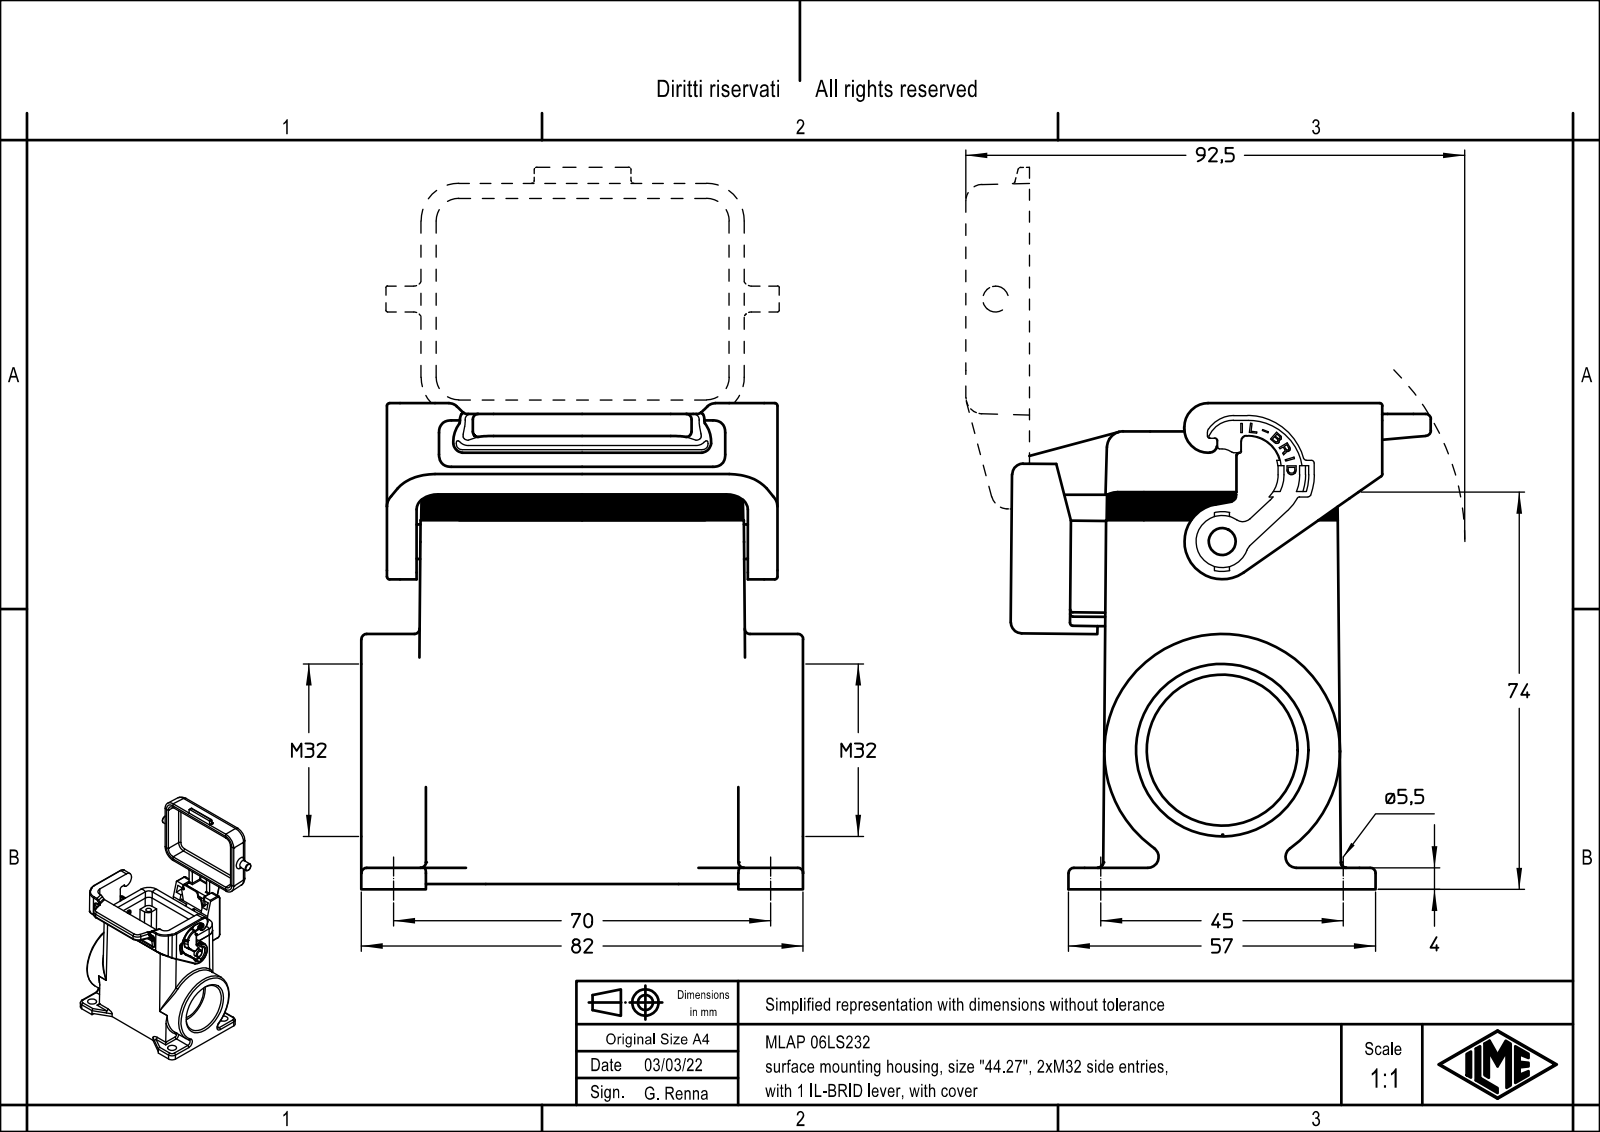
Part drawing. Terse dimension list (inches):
name: MLAP_06LS232
written by: Creo Elements/Direct Modeling 20.1B 02-Apr-2019 (C) Parametric Technology GmbH (AUTOMOTIVE_DESIGN)
unit: in
bodies: 1 solid, 917 faces (566 planar, 263 cylindrical, 88 other)
size: 5.276 × 3.38 × 3.228
volume: 7.503 in³; area: 92.26 in²
holes: 4× ⌀0.138, 4× ⌀0.232, 1× ⌀1.102, 1× ⌀1.205
bosses: 2× ⌀0.189, 1× ⌀1.693, 1× ⌀0.315, 1× ⌀0.252
rounds: 39× R0.039, 21× R0.118, 19× R0.02, 15× R0.013, 13× R0.079, 12× R0.059, 10× R0.276, 4× R0.012
face distances: 1.545, 0.148, 1.693, 1.398, 0.079, 2.553, 0.394, 2.622, 2.474, 1.077
hole spacings: 0.622, 1.507, 2.272, 2.654, 1.063, 1.732, 1.772, 2.032
